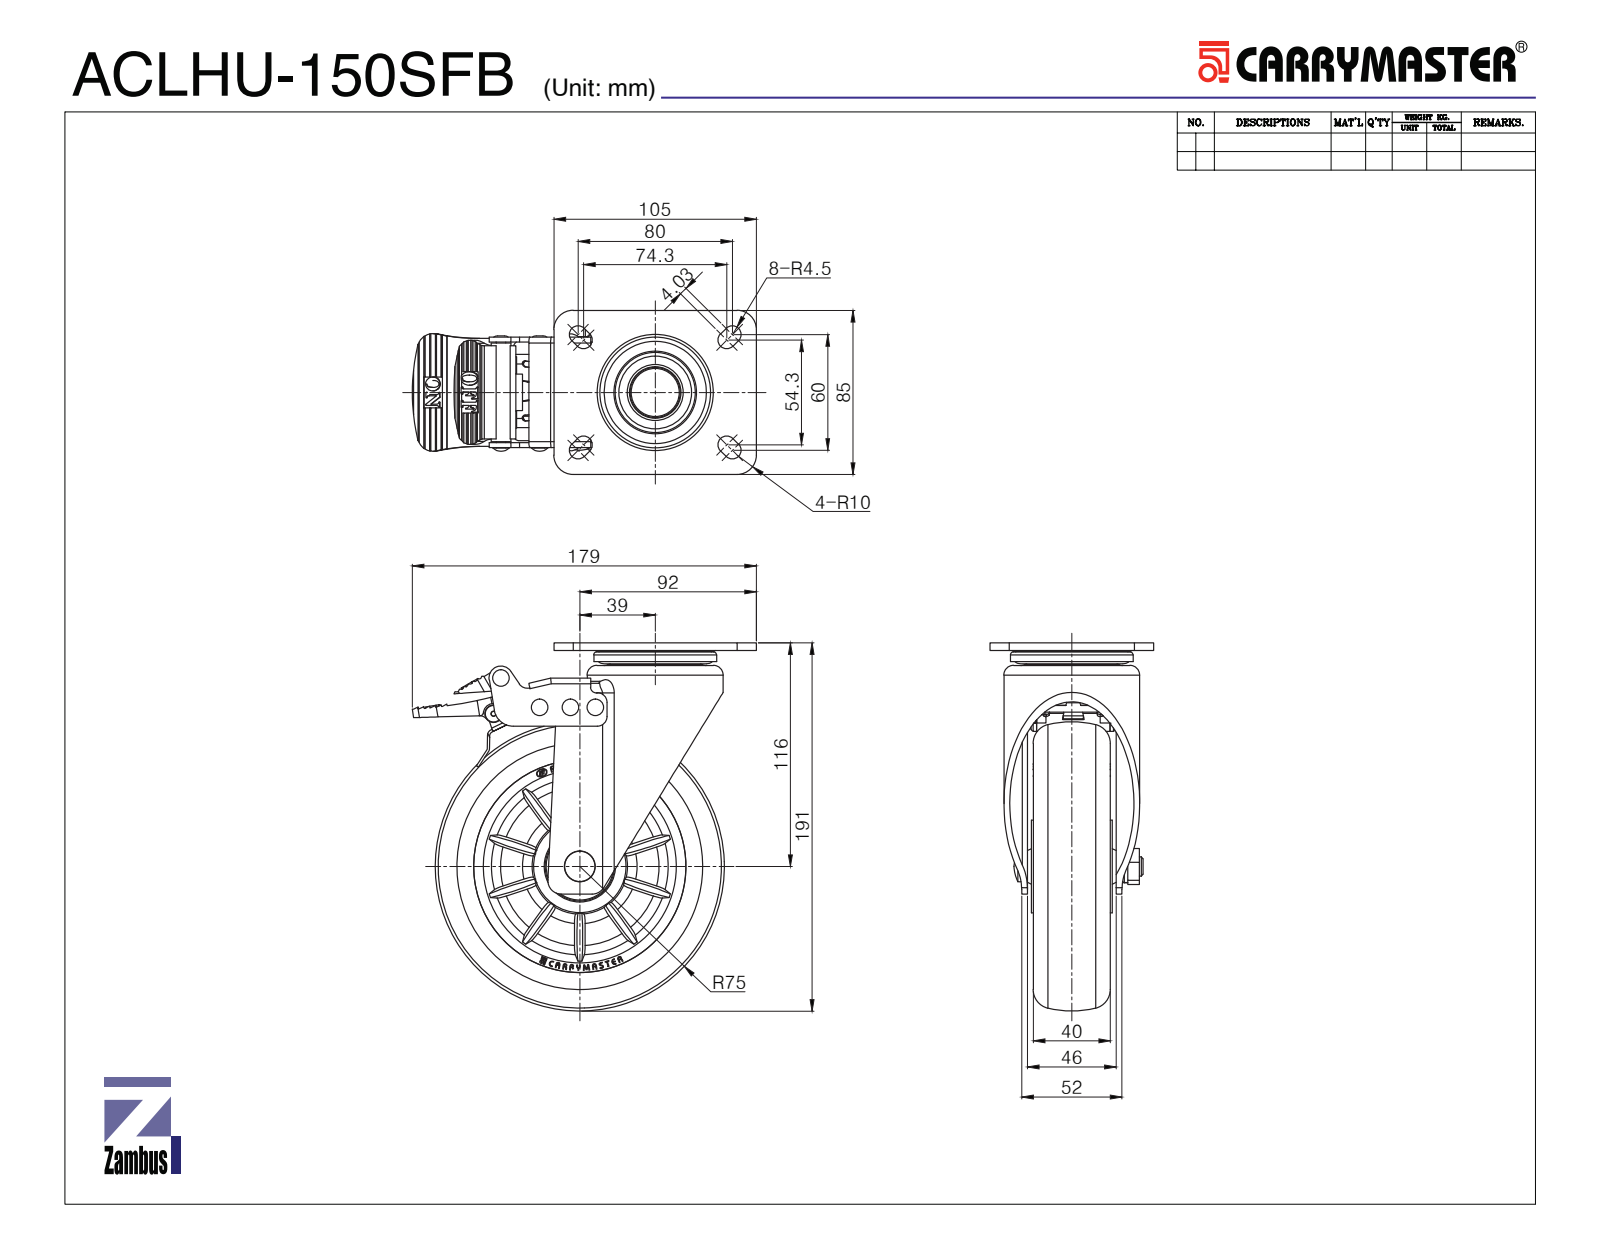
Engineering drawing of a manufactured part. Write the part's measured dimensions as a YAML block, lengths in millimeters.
part_name: "ACLMU-150SFB"
step_written_by: "SolidWorks 2015 (CONFIG_CONTROL_DESIGN)"
units: millimeters
bodies: {solids: 40, faces: 2575, planar: 1387, cylindrical: 556, other: 632}
overall_size: [190.99, 178.55, 85]
volume: 737884
surface_area: 245381
round_holes:
  - {diameter: 1.7, count: 2}
  - {diameter: 3.5, count: 2}
  - {diameter: 4.3, count: 2}
  - {diameter: 5, count: 2}
  - {diameter: 2.5, count: 1}
  - {diameter: 2.6, count: 1}
  - {diameter: 4, count: 1}
  - {diameter: 5.2, count: 1}
  - {diameter: 5.3, count: 1}
  - {diameter: 8.5, count: 1}
  - {diameter: 10, count: 1}
  - {diameter: 12, count: 1}
round_bosses_or_shafts:
  - {diameter: 4.9, count: 4}
  - {diameter: 9, count: 2}
  - {diameter: 6.9, count: 2}
  - {diameter: 0.65, count: 2}
  - {diameter: 130, count: 1}
  - {diameter: 70.42, count: 1}
  - {diameter: 63.7, count: 1}
  - {diameter: 60.5, count: 1}
partial_cylinders:
  - {radius: 1, count: 53}
  - {radius: 3, count: 24}
  - {radius: 22, count: 20}
  - {radius: 1.5, count: 17}
  - {radius: 4.5, count: 8}
  - {radius: 5, count: 7}
  - {radius: 0.5, count: 5}
  - {radius: 10, count: 5}
face_to_face_distances: [3, 6, 4, 46, 23, 43, 40, 49, 5, 18]
hole_center_spacings: [53.3, 0.46, 9.31, 9.7, 12.81, 13, 16, 16.66]
